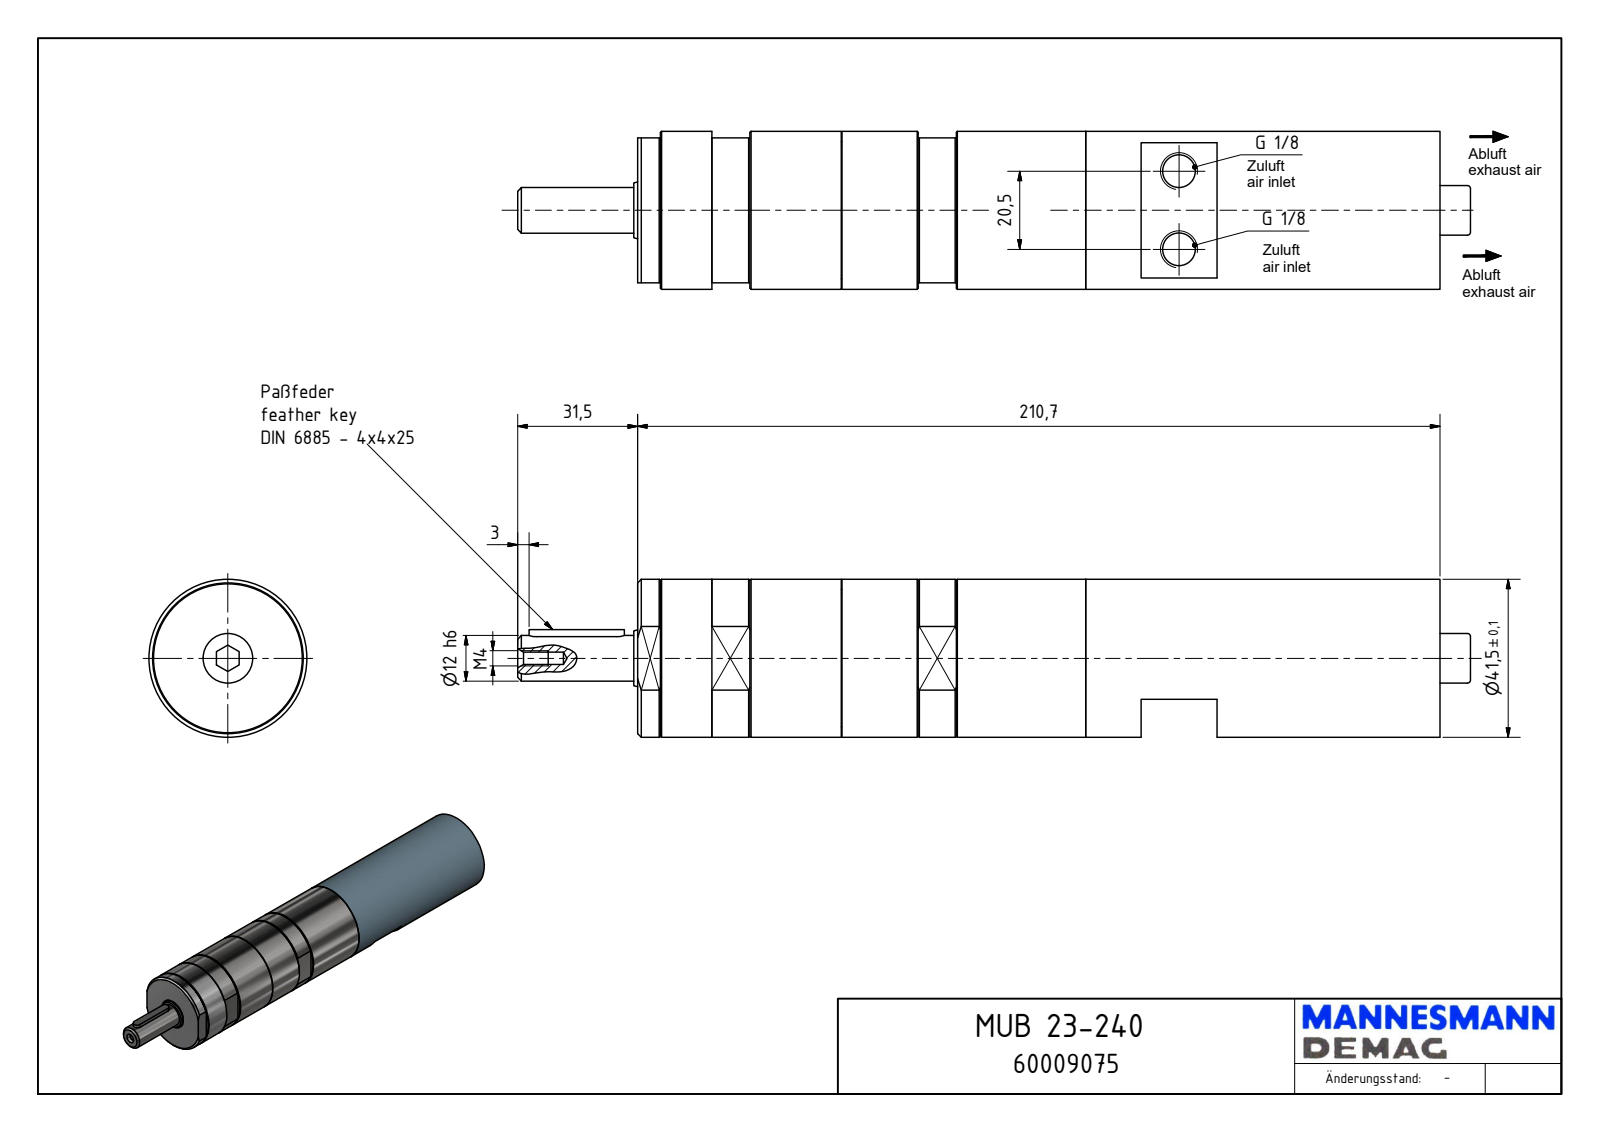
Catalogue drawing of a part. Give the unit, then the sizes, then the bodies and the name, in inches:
Units: inches
Overall size (bounding box): 9.85 × 1.634 × 1.634
Round holes (diameter × count): ⌀0.337 ×2, ⌀0.128 ×1, ⌀0.335 ×1, ⌀0.512 ×1, ⌀0.63 ×1, ⌀1.555 ×1
Round bosses / shafts (diameter × count): ⌀1.634 ×1, ⌀1.535 ×1, ⌀1.417 ×1, ⌀0.589 ×1, ⌀0.472 ×1, ⌀0.315 ×1
Partial cylindrical surfaces — rounded edges, fillets, slot ends (radius × count): R0.079 ×4, R0.039 ×2, R0.063 ×2, R0.098 ×2, R0.319 ×1, R0.5 ×1
Main face-to-face distances: 8.295, 3.091, 1.496, 2.106, 6.189, 2.114, 6.181, 2.303, 0.787, 5.992
Hole centre spacings: 0.807
Volume: 17.18 in³ · Surface area: 55.76 in²
Bodies: 1 solid, 137 faces (62 planar, 51 cylindrical, 24 other)
Part name (STEP PRODUCT): MUB 23-240_60009075
STEP written by: Autodesk Inventor 2018 (AUTOMOTIVE_DESIGN)
